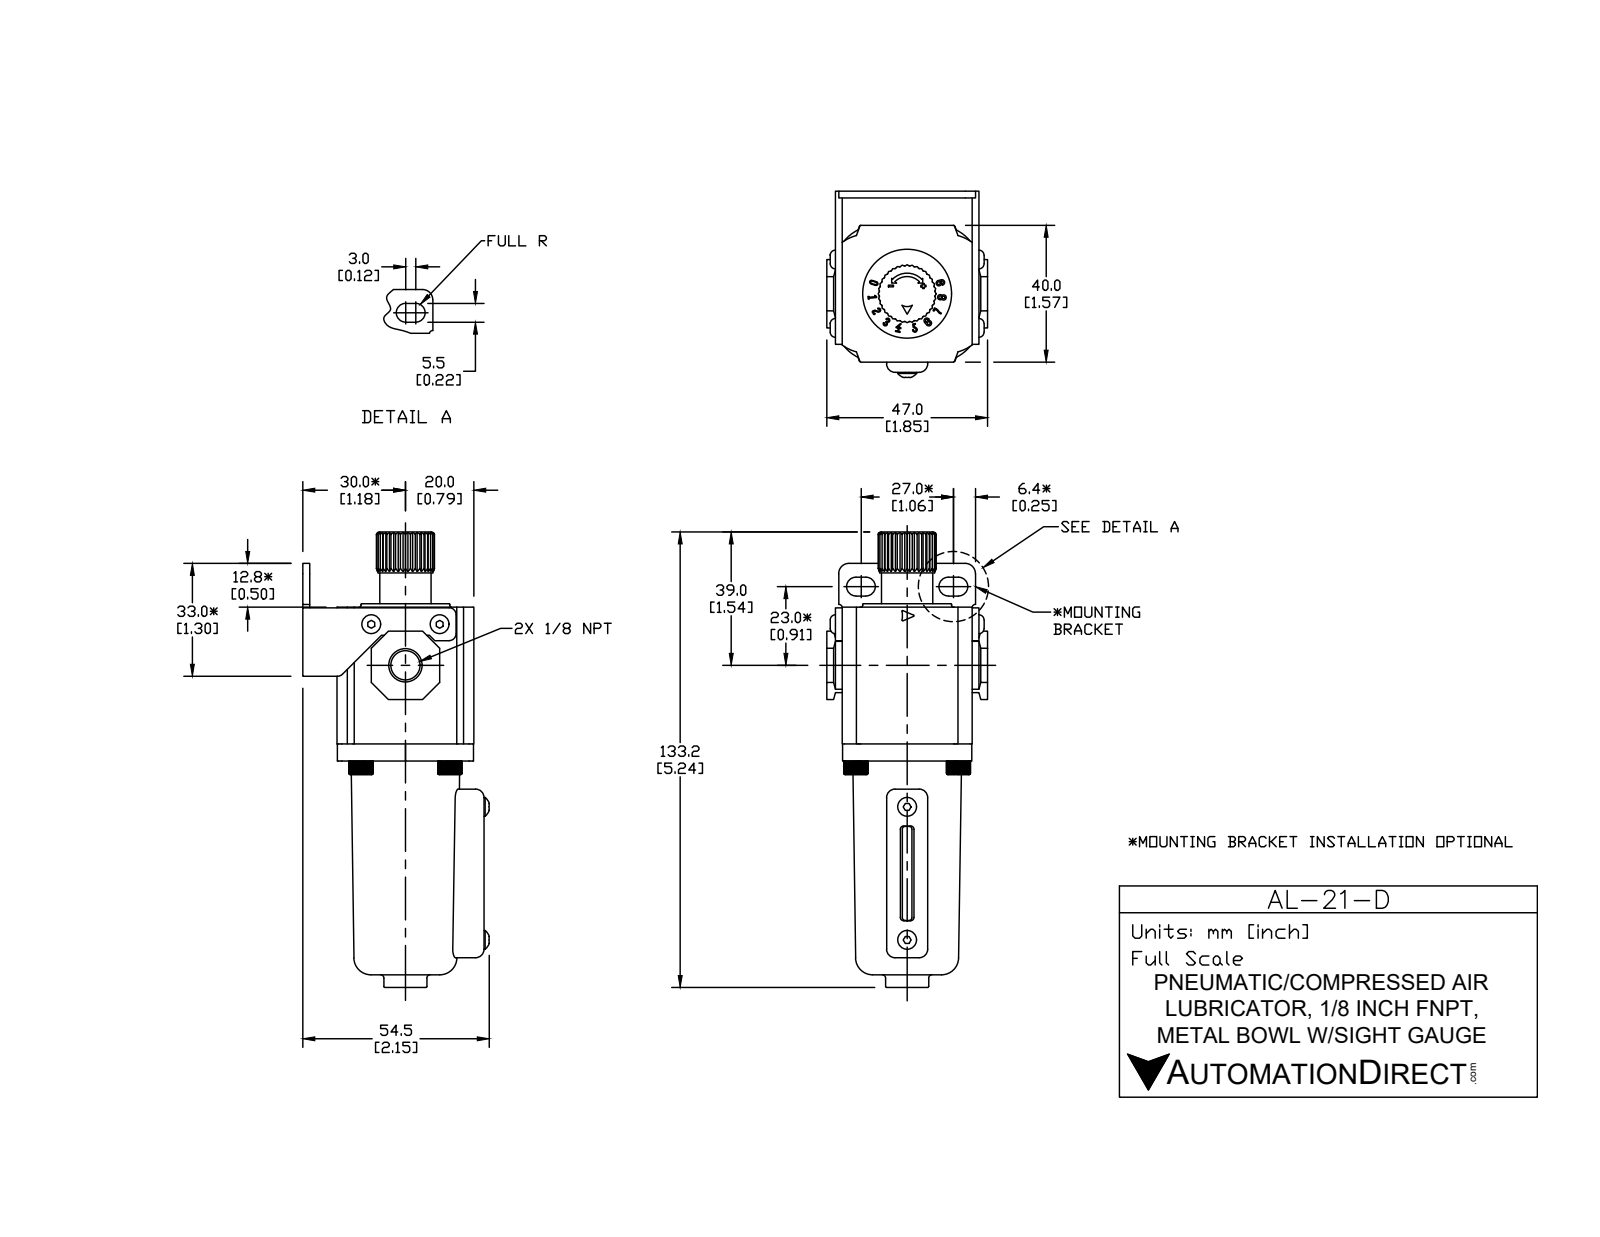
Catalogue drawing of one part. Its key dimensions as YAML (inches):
part_name: "AL-21-D"
step_written_by: "SolidWorks 2015 (CONFIG_CONTROL_DESIGN)"
units: inches
bodies: {solids: 8, faces: 576, planar: 326, cylindrical: 122, other: 128}
overall_size: [5.244, 2.165, 1.85]
volume: 7.628
surface_area: 47.48
round_holes:
  - {diameter: 0.134, count: 2}
  - {diameter: 0.332, count: 1}
round_bosses_or_shafts:
  - {diameter: 0.276, count: 4}
  - {diameter: 0.217, count: 2}
  - {diameter: 1.024, count: 1}
  - {diameter: 0.591, count: 1}
  - {diameter: 0.496, count: 1}
partial_cylinders:
  - {radius: 0.012, count: 12}
  - {radius: 0.051, count: 8}
  - {radius: 0.098, count: 8}
  - {radius: 0.079, count: 5}
  - {radius: 0.02, count: 4}
  - {radius: 0.039, count: 4}
  - {radius: 0.106, count: 4}
  - {radius: 0.469, count: 4}
face_to_face_distances: [1.575, 0.079, 1.496, 0.315, 0.394, 1.969, 1.89, 0.047, 0.512, 0.591]
hole_center_spacings: [0.615, 0.787]
